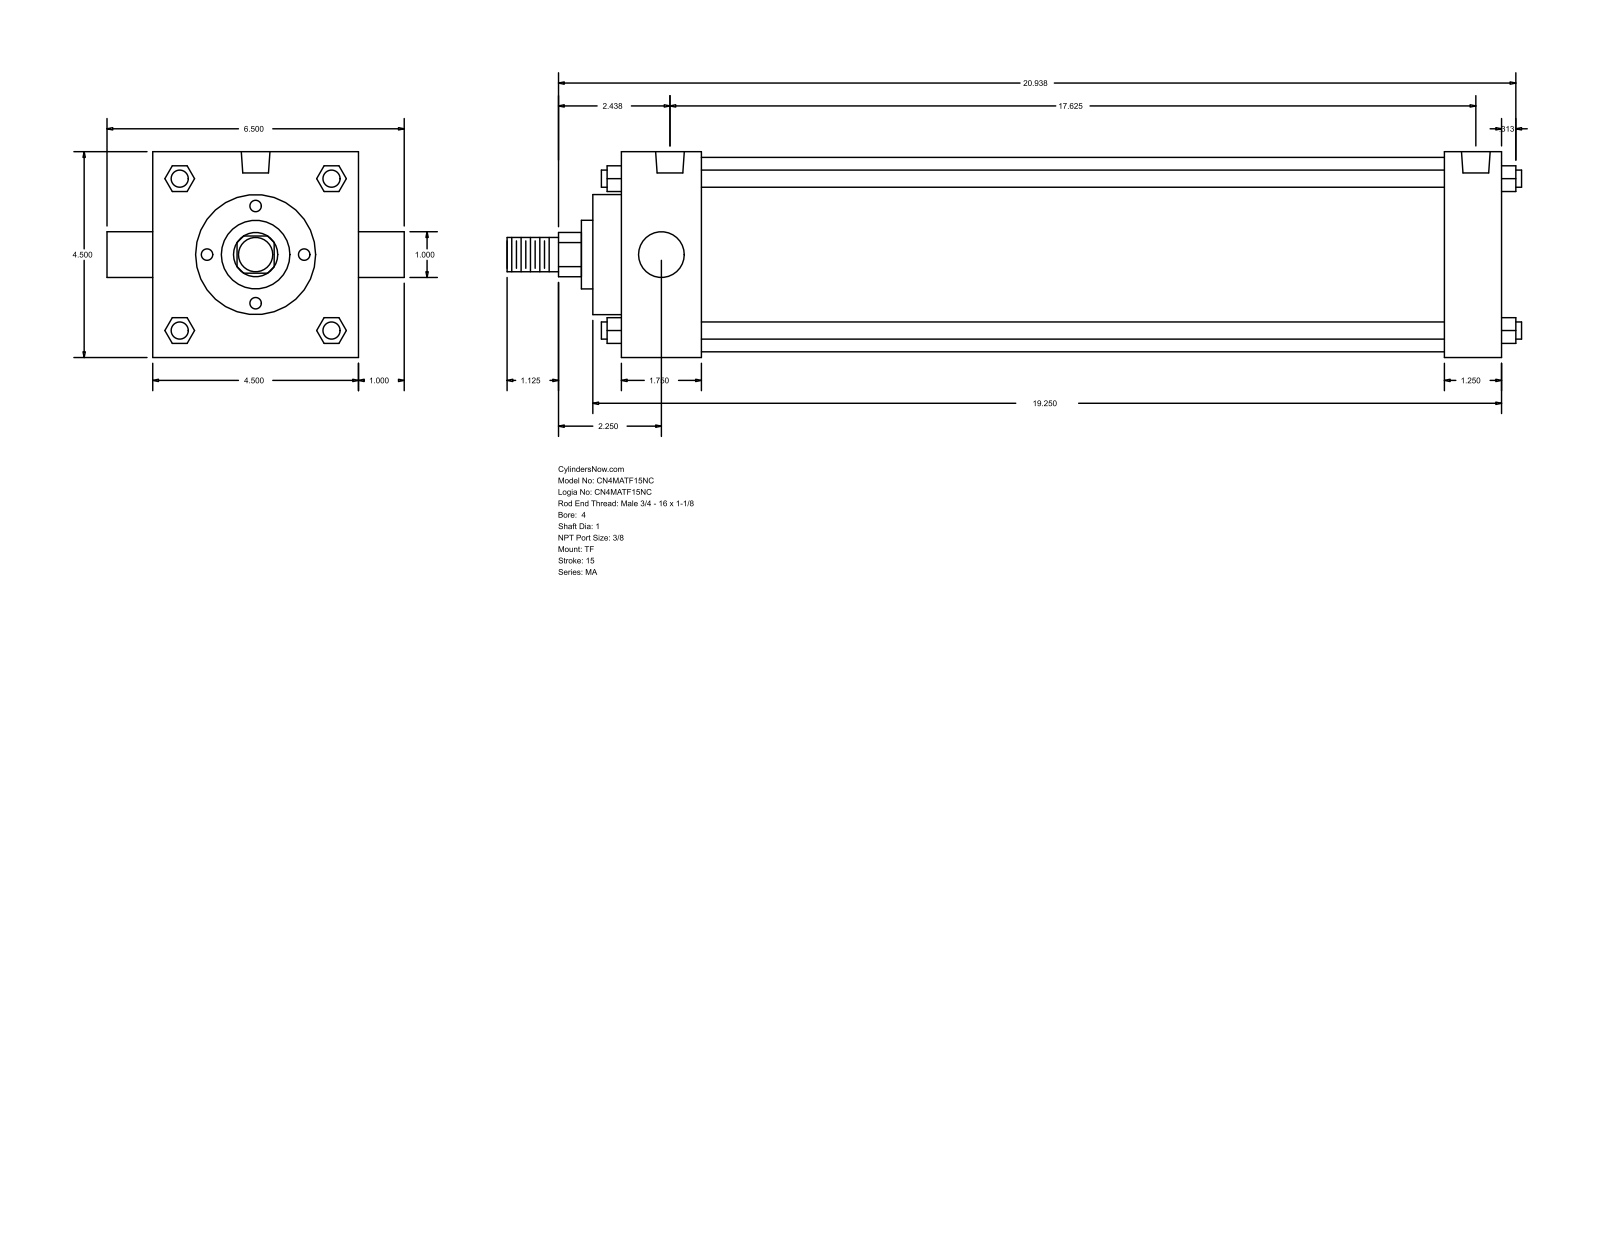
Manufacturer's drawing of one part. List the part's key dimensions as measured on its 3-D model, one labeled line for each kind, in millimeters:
Part name (STEP PRODUCT): MA_TF__0400_1
STEP written by: GSSL Pune (CONFIG_CONTROL_DESIGN)
Units: millimetres
Bodies: 0 solids, 122 faces (93 planar, 29 cylindrical, 0 other)
Overall size (bounding box): 563.56 × 165.1 × 114.3
Round holes (diameter × count): ⌀11.11 ×3, ⌀15.93 ×2
Round bosses / shafts (diameter × count): ⌀9.53 ×4, ⌀25.4 ×2, ⌀107.95 ×1, ⌀66.67 ×1, ⌀38.1 ×1, ⌀19.05 ×1
Partial cylindrical surfaces — rounded edges, fillets, slot ends (radius × count): R12.29 ×1
Main face-to-face distances: 114.3, 488.96, 457.2, 31.76, 44.46, 412.74, 444.5, 15.87, 60.33, 473.07
Hole centre spacings: 4.76, 4.77, 438.15, 442.91, 442.92, 447.68
